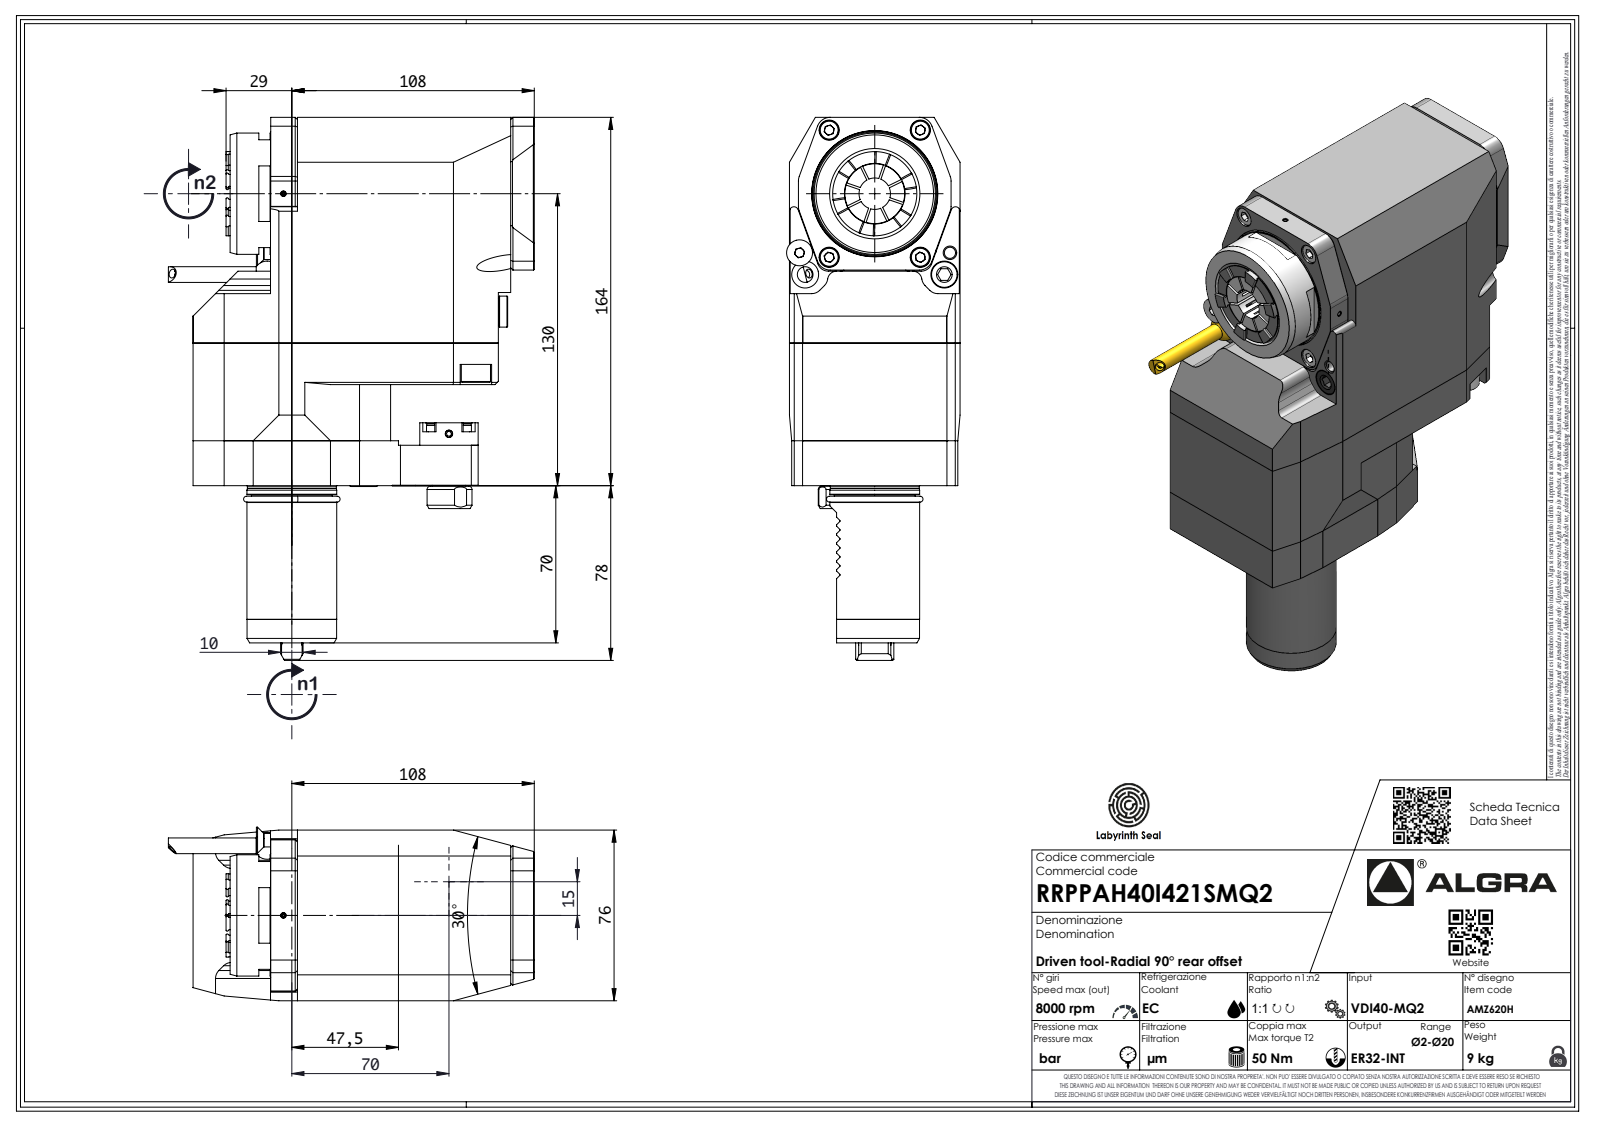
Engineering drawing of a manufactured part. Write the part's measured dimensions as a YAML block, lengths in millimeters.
part_name: "RRPPAH40I421SMQ2"
step_written_by: "SolidWorks 2023 (AUTOMOTIVE_DESIGN)"
units: millimeters
bodies: {solids: 2, faces: 670, planar: 416, cylindrical: 118, other: 136}
overall_size: [241.8, 163.5, 76]
volume: 1503000
surface_area: 102461
round_holes:
  - {diameter: 2.1, count: 1}
  - {diameter: 4, count: 1}
round_bosses_or_shafts:
  - {diameter: 54, count: 1}
  - {diameter: 40, count: 1}
  - {diameter: 39.9, count: 1}
  - {diameter: 39.6, count: 1}
  - {diameter: 36, count: 1}
  - {diameter: 26, count: 1}
  - {diameter: 20, count: 1}
  - {diameter: 15, count: 1}
partial_cylinders:
  - {radius: 6, count: 10}
  - {radius: 1, count: 8}
  - {radius: 3, count: 8}
  - {radius: 0.3, count: 7}
  - {radius: 0.33, count: 7}
  - {radius: 0.52, count: 7}
  - {radius: 3.7, count: 7}
  - {radius: 5, count: 6}
face_to_face_distances: [76, 164, 136, 16.5, 45, 119, 152.5, 88, 119.5, 68.5]
